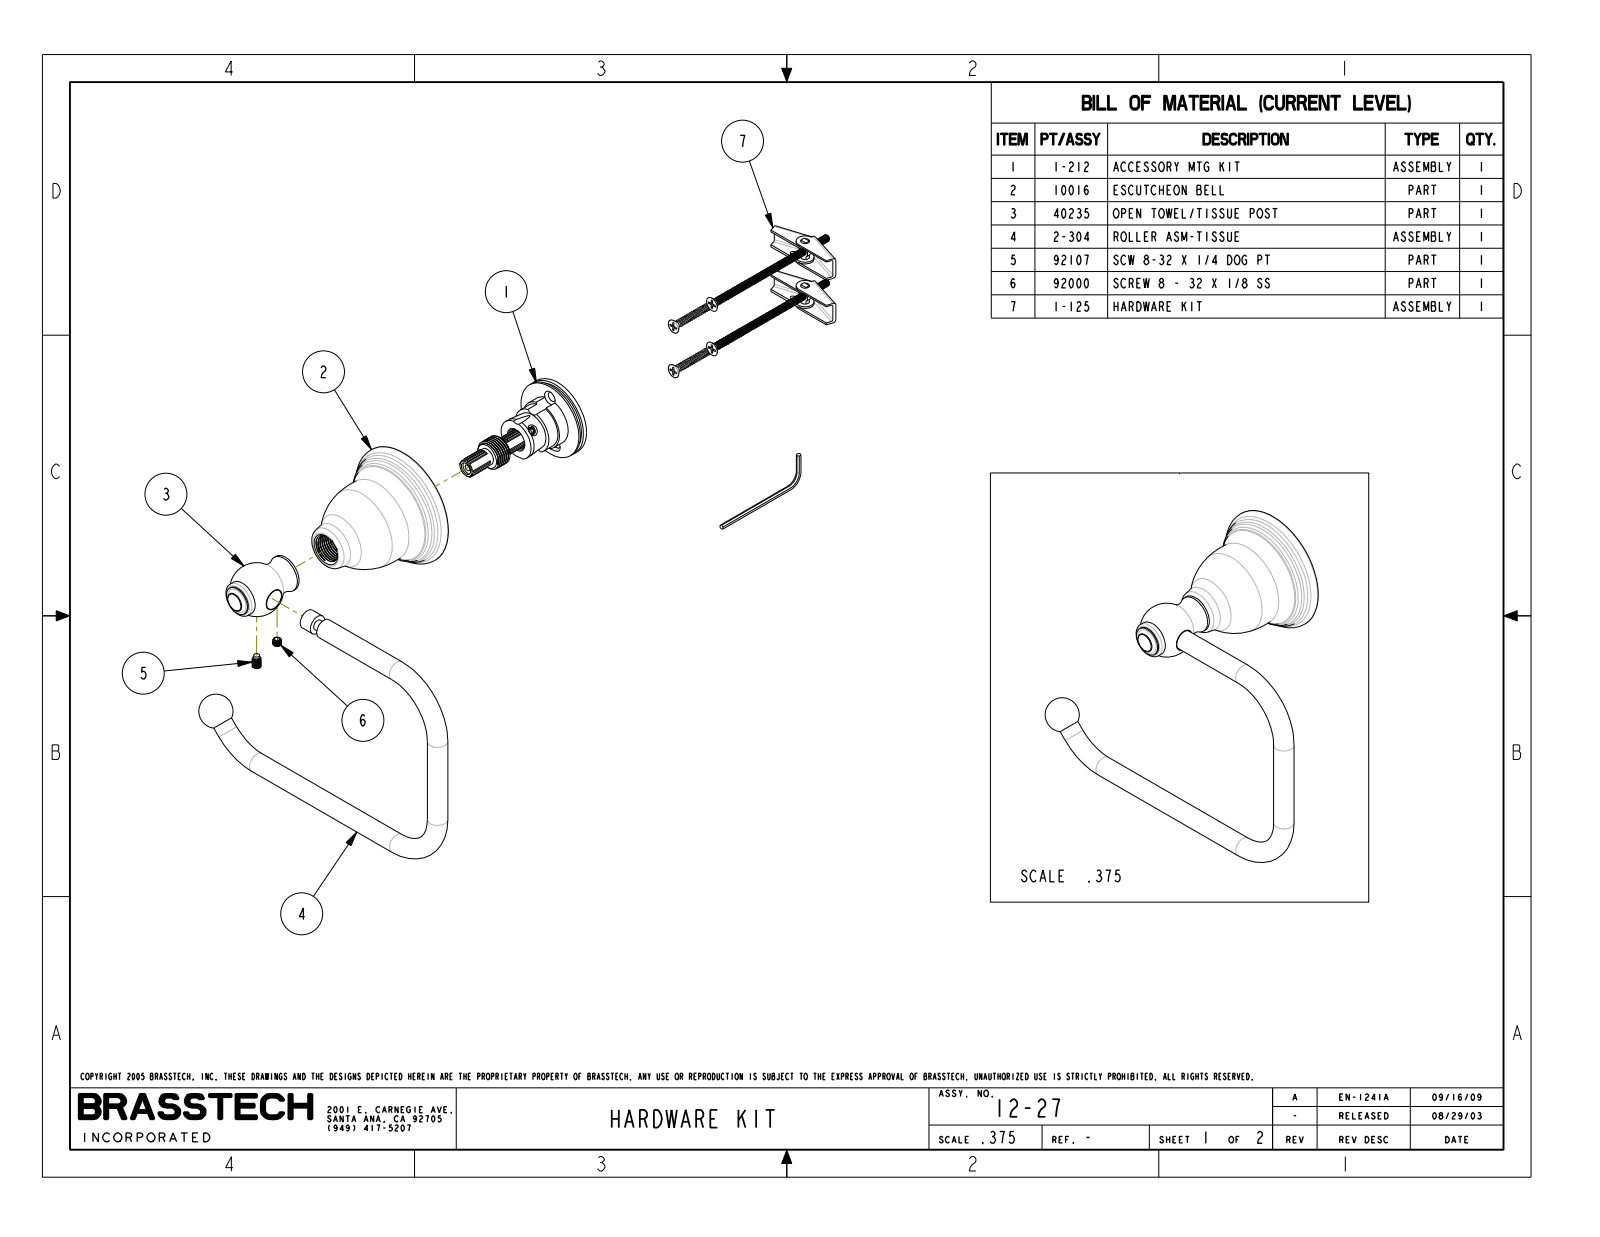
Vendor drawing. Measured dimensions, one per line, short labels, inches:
name: 12-27_WEB
written by: PRO/ENGINEER BY PARAMETRIC TECHNOLOGY CORPORATION, 2009300 (CONFIG_CONTROL_DESIGN)
unit: in
bodies: 0 solids, 79 faces (8 planar, 18 cylindrical, 53 other)
size: 6.247 × 5.233 × 3.333
bosses: 4× ⌀0.375, 1× ⌀2.34, 1× ⌀0.705, 1× ⌀0.661, 1× ⌀0.545
face distances: 3.243, 3.267, 0.024, 3.333, 0.09, 0.066, 0.2
